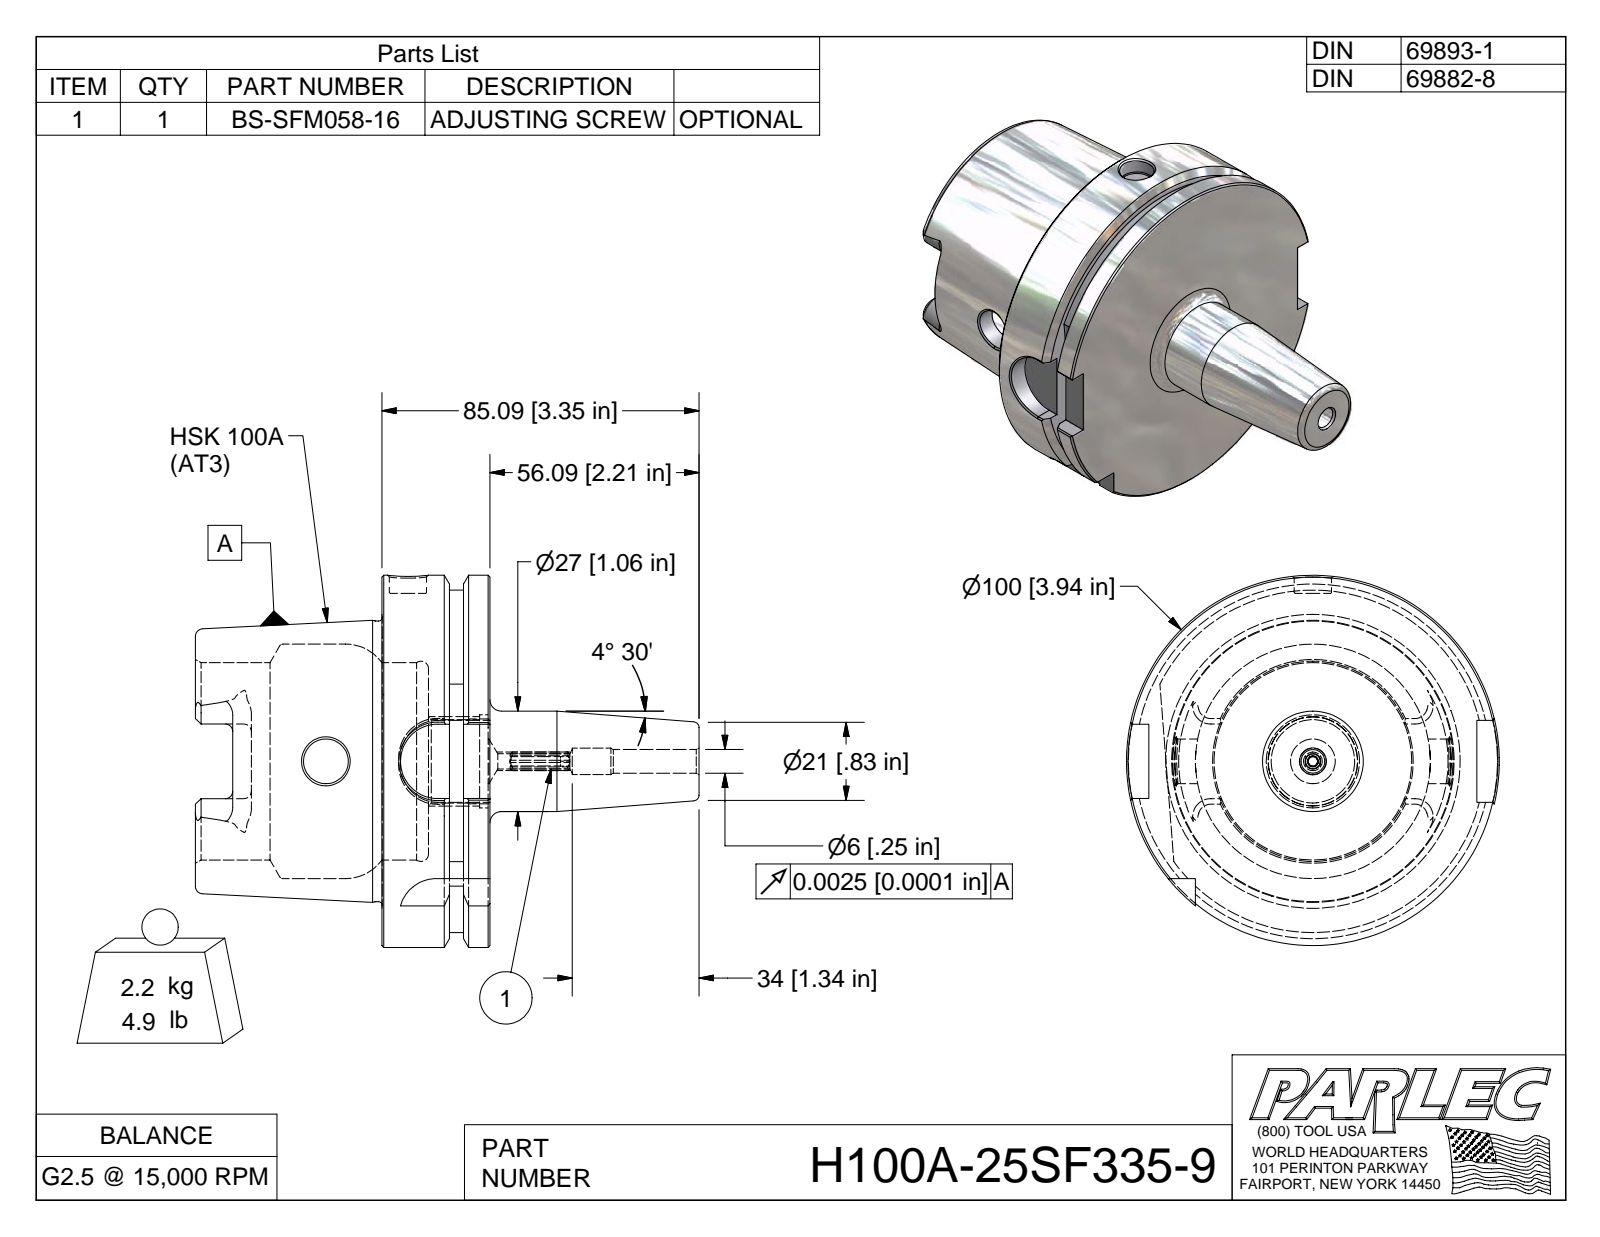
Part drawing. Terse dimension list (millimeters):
name: H100A-25SF335-9; H100A-25SF335-9-1; BS-SFM058-16
written by: Autodesk Inventor 2009 (AUTOMOTIVE_DESIGN)
unit: mm
bodies: 2 solids, 149 faces (49 planar, 30 cylindrical, 70 other)
size: 135.1 × 100 × 100
volume: 280 200 mm³; area: 55 460 mm²
holes: 1× ⌀6.4, 1× ⌀7.1, 1× ⌀10, 1× ⌀12, 1× ⌀22.4, 1× ⌀25, 1× ⌀53, 1× ⌀63
bosses: 1× ⌀100, 1× ⌀75.4, 1× ⌀27
rounds: 4× R10, 3× R2, 2× R4.9, 1× R2.5, 1× R46
face distances: 29, 12.5, 16.5, 50, 62.5, 79, 68.1, 18.1, 5.6, 10.9
